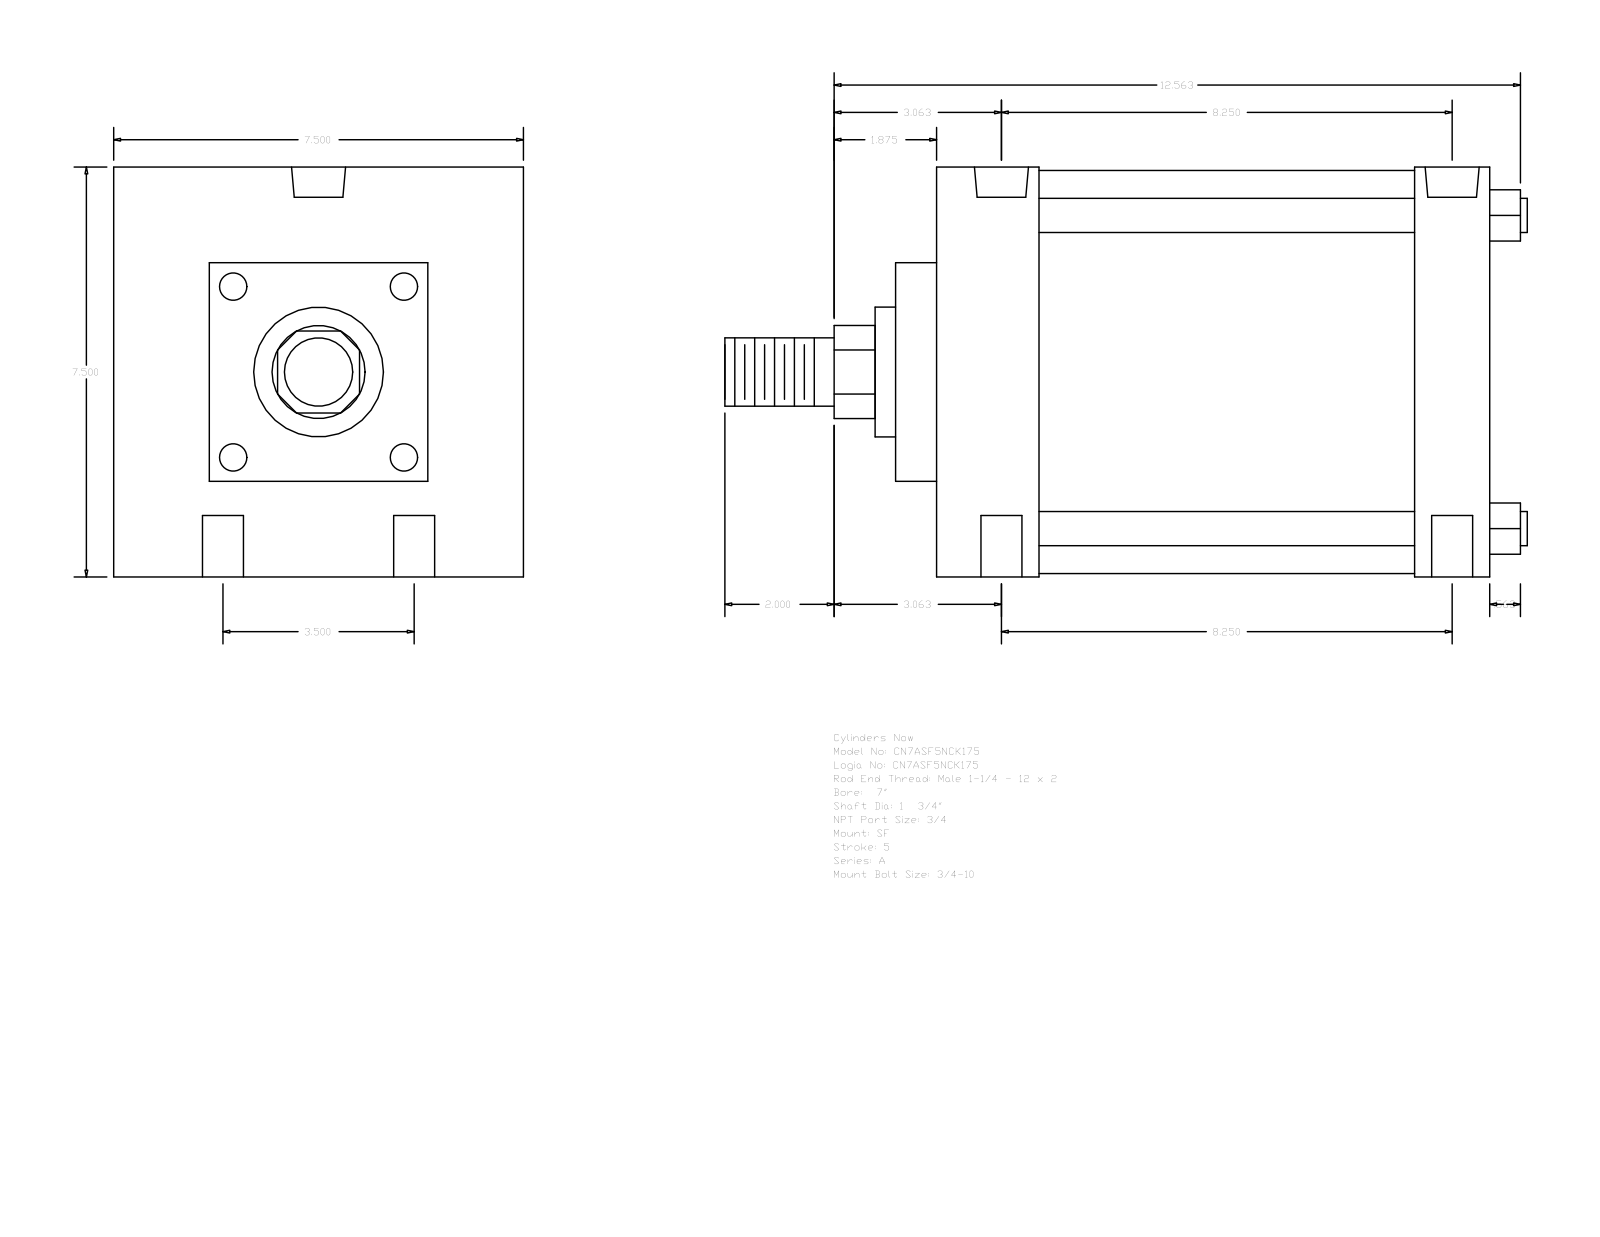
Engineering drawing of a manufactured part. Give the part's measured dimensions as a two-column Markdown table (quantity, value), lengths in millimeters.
| quantity | value |
| --- | --- |
| part name | A_SF__0700_1.75 |
| STEP written by | GSSL Pune (CONFIG_CONTROL_DESIGN) |
| units | millimeters |
| bodies | 0 solids, 93 faces (67 planar, 26 cylindrical, 0 other) |
| overall size | 373.06 × 190.5 × 190.5 |
| round holes (diameter × count) | 19.05 × 4, 15.08 × 2, 25.12 × 2 |
| round bosses / shafts (diameter × count) | 15.88 × 4, 187.32 × 1, 60.33 × 1, 44.45 × 1, 31.75 × 1 |
| partial cylindrical surfaces (radius × count) | 21.63 × 1 |
| main face-to-face distances | 190.5, 257.18, 146.05, 19.05, 47.63, 222.26, 174.63, 209.55, 34.92, 44.45 |
| hole center spacings | 44.45, 214.21, 209.55, 88.9, 227.63, 198.43 |
